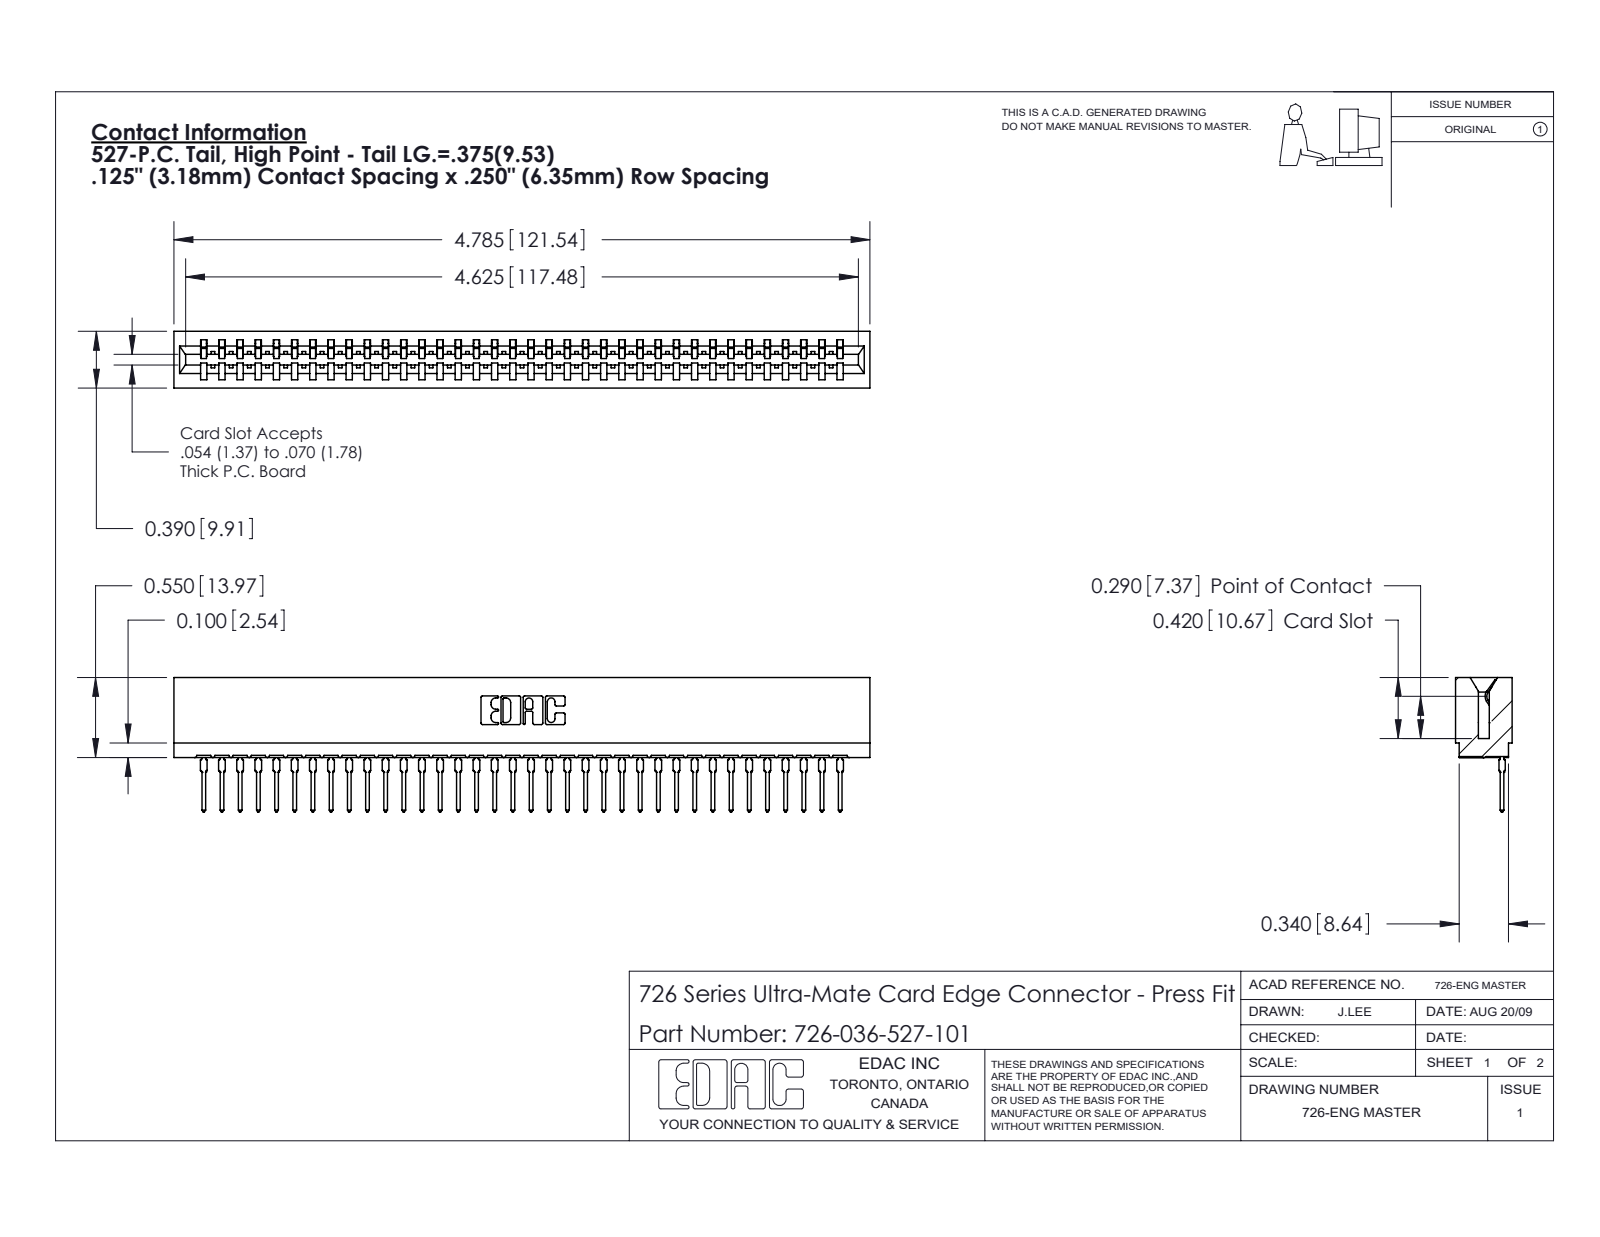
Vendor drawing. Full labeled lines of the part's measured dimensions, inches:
Part name (STEP PRODUCT): 746-292-001_527; 726-036-527-101; 726 Part_.515 Slot Depth - 01
STEP written by: SolidWorks 2020 (CONFIG_CONTROL_DESIGN)
Units: inches
Bodies: 37 solids, 3985 faces (2323 planar, 726 cylindrical, 936 other)
Overall size (bounding box): 4.785 × 0.924 × 0.39
Volume: 0.666 in³ · Surface area: 26.01 in²
Partial cylindrical surfaces — rounded edges, fillets, slot ends (radius × count): R0.021 ×72, R0.015 ×37, R0.01 ×22, R0.007 ×6, R0.031 ×6, R0.005 ×4, R0.011 ×4, R0.026 ×3
Main face-to-face distances: 0.057, 0.333, 0.39, 0.25, 0.025, 0.307, 0.083, 0.275, 0.5, 0.365
